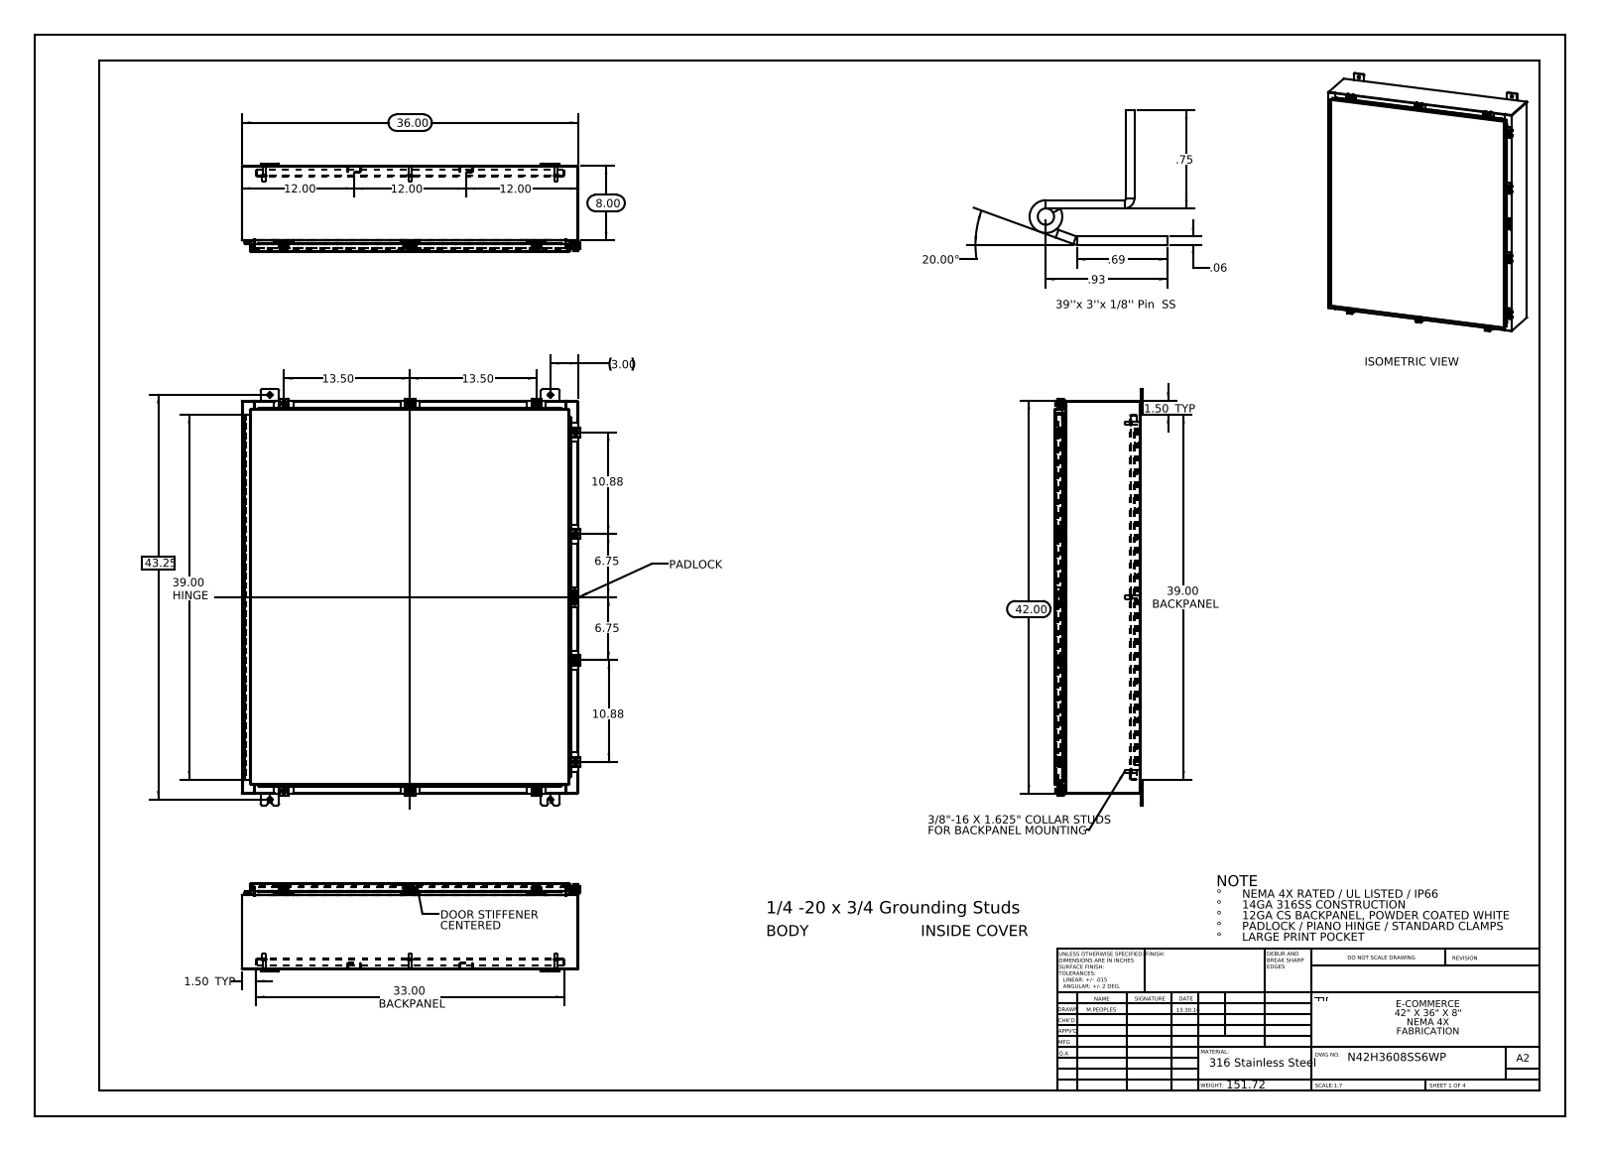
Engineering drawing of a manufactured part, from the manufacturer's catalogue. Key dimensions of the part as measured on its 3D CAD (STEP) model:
Part name (STEP PRODUCT): N42H3608SS6WP Standard Clamps; N42H3608SS6WP 22101002; N42H3608SS6WP Hinge Enclosure Side2; N42H3608SS6WP Body (+8 more)
STEP written by: SolidWorks 2013 (CONFIG_CONTROL_DESIGN)
Units: inches
Bodies: 74 solids, 2855 faces (1490 planar, 1197 cylindrical, 168 other)
Overall size (bounding box): 44.5 × 36.211 × 9.389
Volume: 532 in³ · Surface area: 13 223 in²
Round holes (diameter × count): ⌀0.5 ×12, ⌀0.213 ×10, ⌀0.26 ×10, ⌀0.25 ×6, ⌀0.125 ×2, ⌀0.125 ×1
Round bosses / shafts (diameter × count): ⌀0.25 ×11, ⌀0.5 ×10, ⌀0.399 ×10, ⌀0.625 ×8, ⌀0.375 ×8, ⌀0.33 ×8
Partial cylindrical surfaces — rounded edges, fillets, slot ends (radius × count): R0.06 ×46, R0.013 ×39, R0.088 ×33, R0.19 ×24, R0.12 ×20, R0.141 ×20, R0.05 ×15, R0.08 ×14
Main face-to-face distances: 0.075, 9.126, 9.051, 9.201, 0.104, 1, 8.126, 1.075, 8.051, 1.179
Hole centre spacings: 13.5, 13.663, 17, 17.145, 18.625, 20.834, 24.311, 25.956
